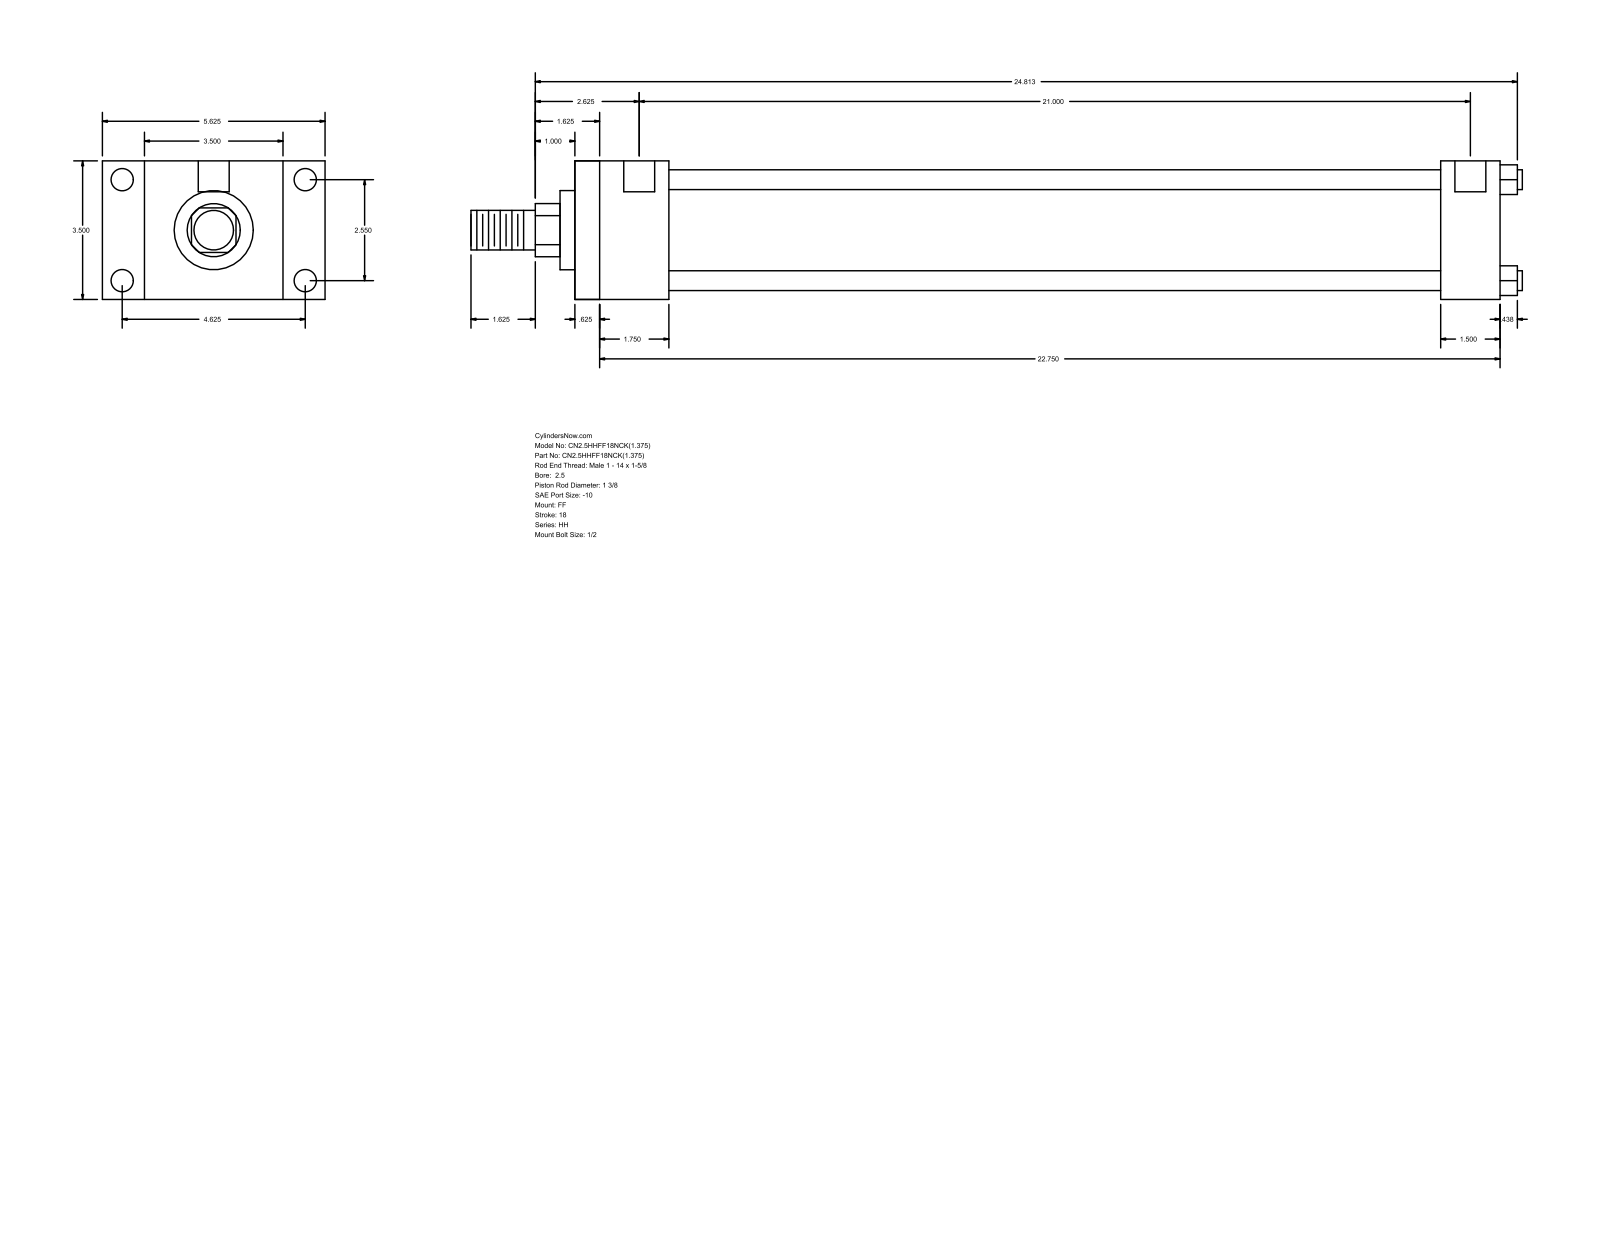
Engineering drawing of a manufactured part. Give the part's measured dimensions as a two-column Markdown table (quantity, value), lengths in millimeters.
| quantity | value |
| --- | --- |
| part name | HH_FF__0250_1.375 |
| STEP written by | GSSL Pune (CONFIG_CONTROL_DESIGN) |
| units | millimeters |
| bodies | 0 solids, 92 faces (64 planar, 28 cylindrical, 0 other) |
| overall size | 674.69 × 142.88 × 88.9 |
| round holes (diameter × count) | 5.56 × 4, 14.3 × 4, 19.84 × 2 |
| round bosses / shafts (diameter × count) | 12.7 × 4, 73.03 × 1, 50.8 × 1, 34.92 × 1, 25.4 × 1 |
| partial cylindrical surfaces (radius × count) | 17.06 × 1 |
| main face-to-face distances | 88.9, 593.72, 15.87, 577.85, 60.32, 44.45, 533.4, 555.62, 539.75, 495.3 |
| hole center spacings | 1.58, 64.76, 117.48, 134.15, 534.99, 536.57, 533.41 |
